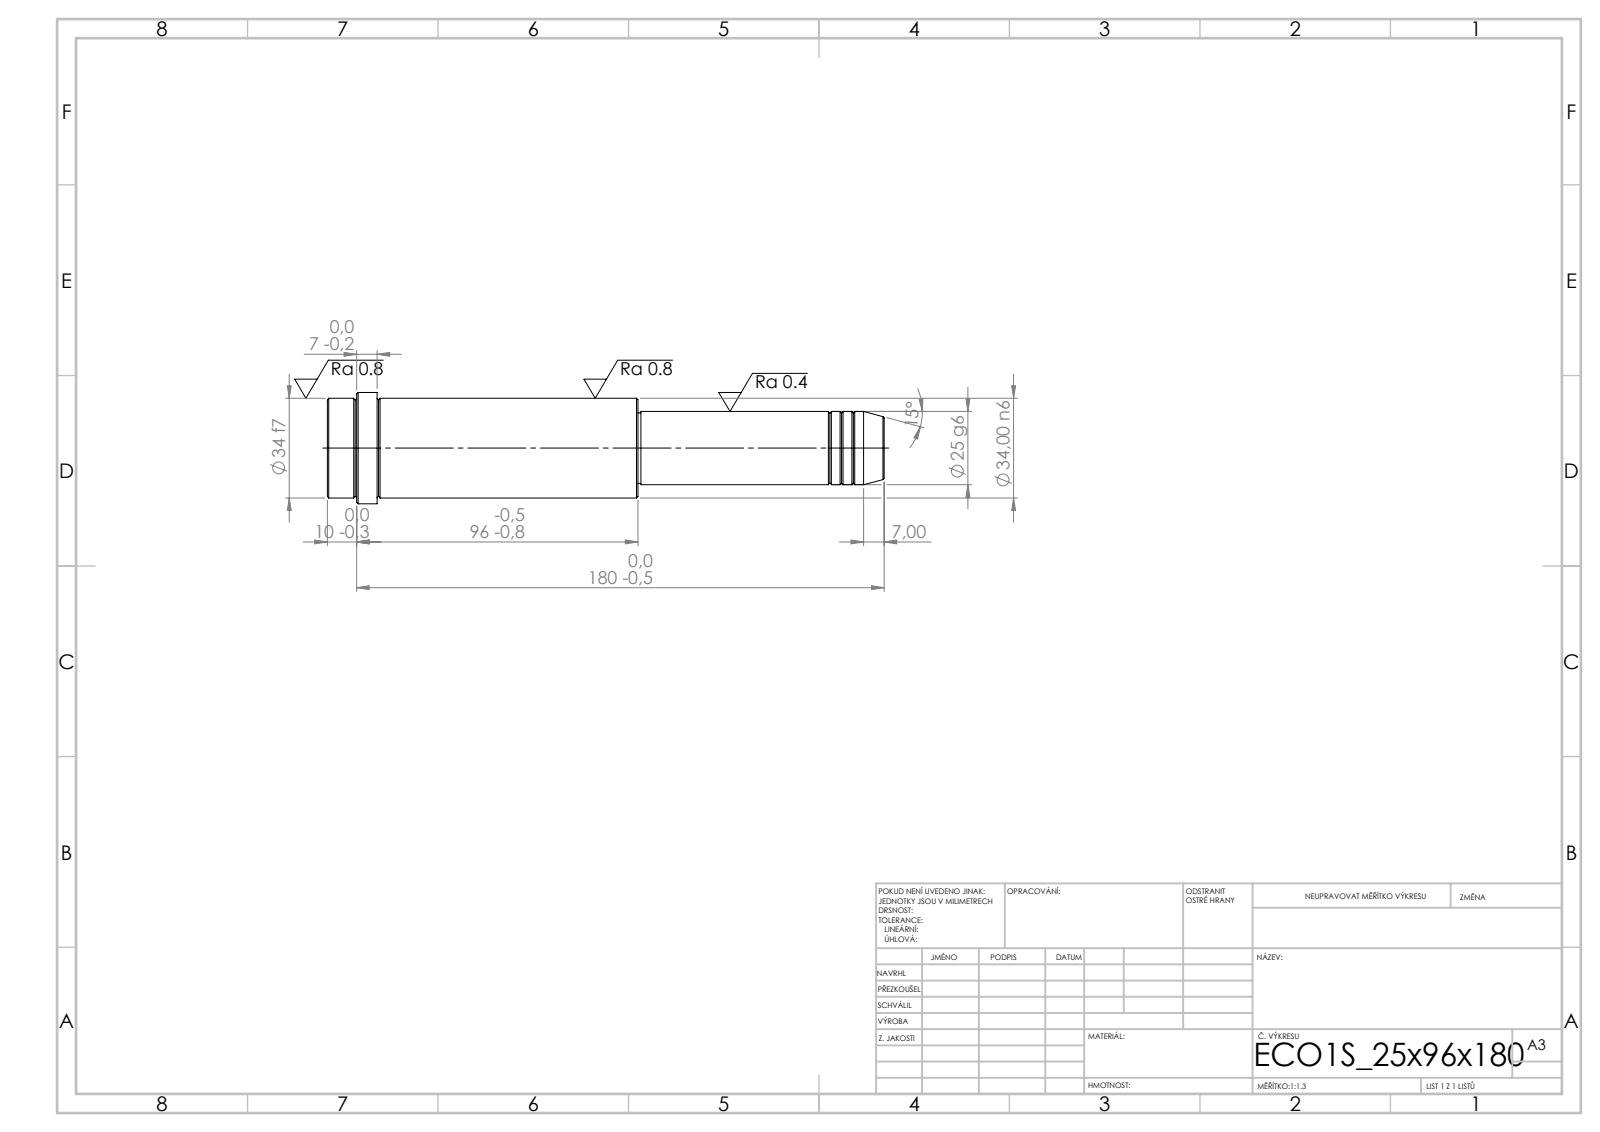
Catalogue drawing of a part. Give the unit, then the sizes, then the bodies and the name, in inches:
Units: inches
Overall size (bounding box): 7.48 × 1.496 × 1.496
Round bosses / shafts (diameter × count): ⌀1.496 ×1, ⌀1.339 ×1, ⌀0.984 ×1, ⌀0.945 ×1
Main face-to-face distances: 4.173, 3.307, 7.48, 6.811, 3.504, 0.669, 7.087, 3.78, 0.276, 0.394
Volume: 8.44 in³ · Surface area: 31.5 in²
Bodies: 1 solid, 52 faces (6 planar, 16 cylindrical, 30 other)
STEP written by: SolidWorks 2019 (CONFIG_CONTROL_DESIGN)
